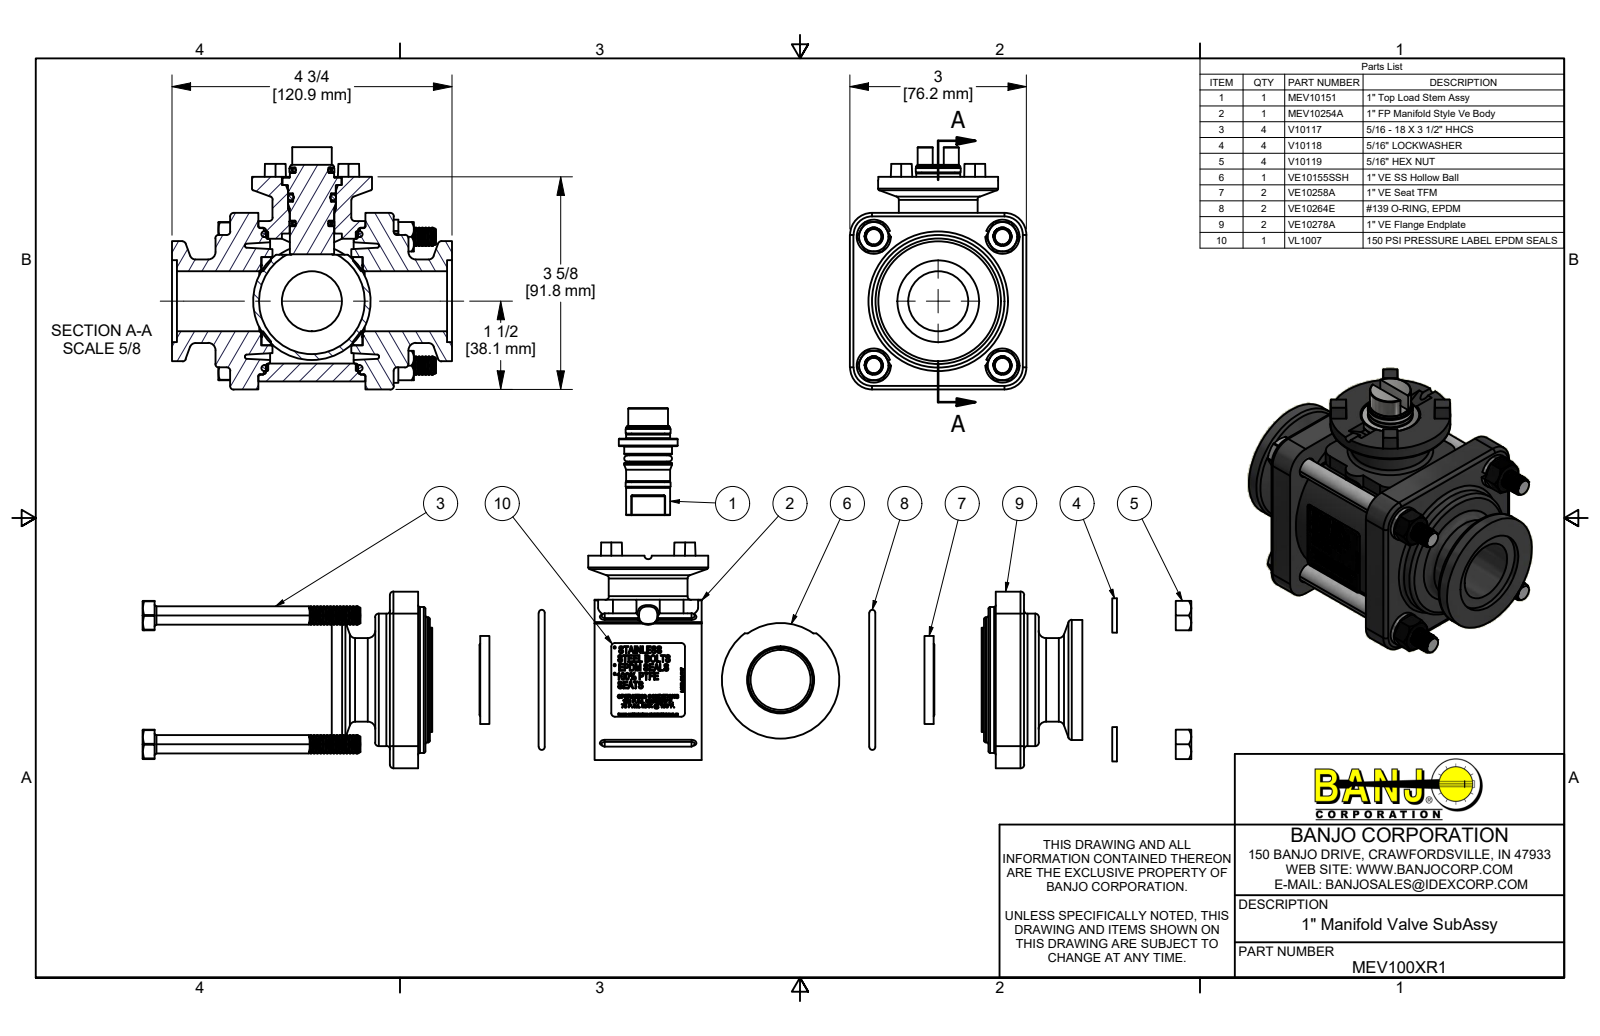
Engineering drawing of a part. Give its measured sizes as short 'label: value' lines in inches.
name: MEV100XR1; MEV10254A; MEV10254AX; VE10155SSH (+8 more)
written by: Autodesk Inventor 2019 (AUTOMOTIVE_DESIGN)
unit: in
bodies: 27 solids, 3087 faces (1343 planar, 497 cylindrical, 1247 other)
size: 4.76 × 4.118 × 3
volume: 20.16 in³; area: 194.2 in²
holes: 4× ⌀0.252, 4× ⌀0.322, 4× ⌀0.35, 3× ⌀1.02, 1× ⌀0.645, 1× ⌀0.76, 1× ⌀0.818, 1× ⌀1.39, 1× ⌀1.5, 1× ⌀2.12, 1× ⌀2.375, 1× ⌀2.5
bosses: 60× ⌀0.268, 4× ⌀0.583, 4× ⌀0.313, 2× ⌀2.04, 1× ⌀2.725, 1× ⌀2.48, 1× ⌀2.25, 1× ⌀2.124
rounds: 16× R0.06, 9× R0.062, 8× R0.01, 8× R0.03, 8× R0.134, 8× R0.375, 4× R0.21, 4× R0.25
face distances: 0.48, 2.3, 1.82, 2.78, 3, 0.99, 1.47, 3.29, 3.77, 0.73
hole spacings: 1.547, 2.188, 3.094
